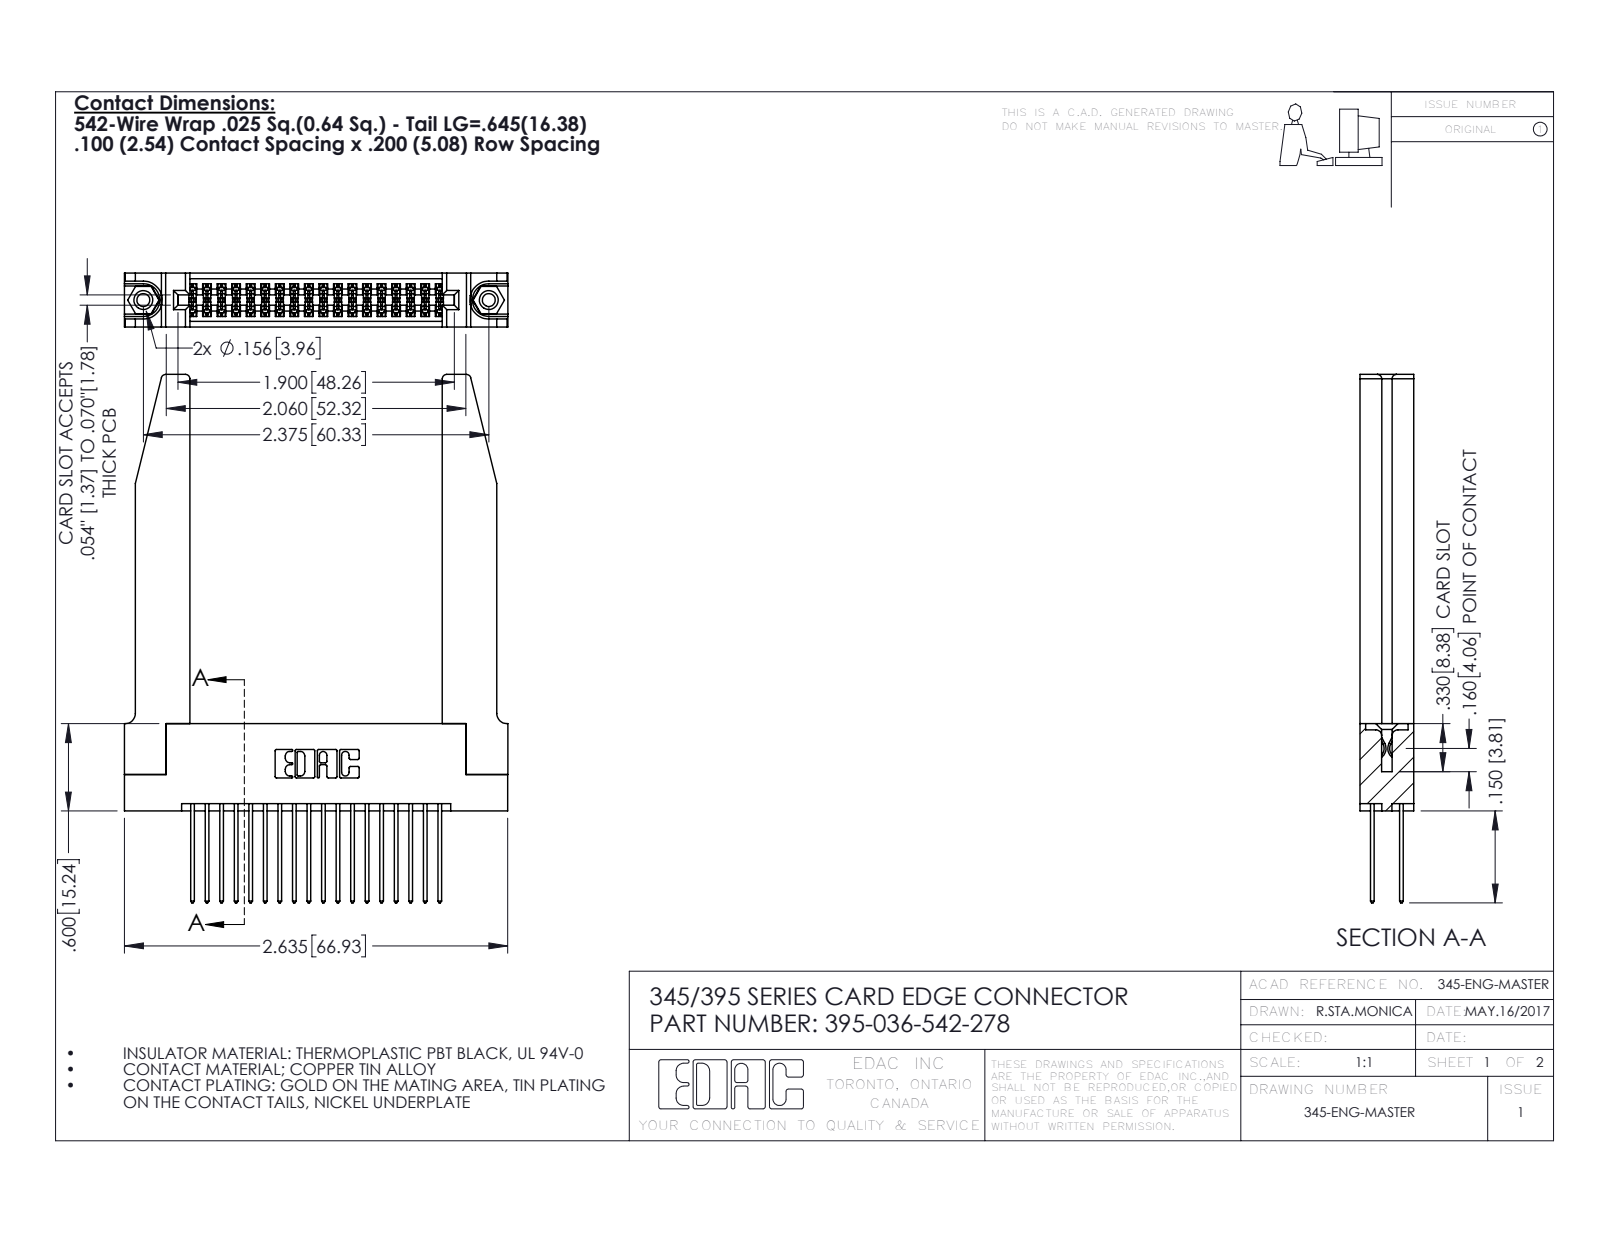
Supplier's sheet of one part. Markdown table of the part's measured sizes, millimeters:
| quantity | value |
| --- | --- |
| part name | 345-250-001_345-250-001-102; 345 Part_Flush Mounting Lugs - 0.156 Dia-TH; 345-220-078_345-220-078; 395-036-542-278 (+1 more) |
| STEP written by | SolidWorks 2016 (CONFIG_CONTROL_DESIGN) |
| units | millimeters |
| bodies | 41 solids, 2160 faces (1410 planar, 698 cylindrical, 52 other) |
| overall size | 92.3 × 67 × 9.4 |
| volume | 14 200 mm³ |
| surface area | 16 690 mm² |
| round holes (diameter × count) | 2.3 × 2, 3.2 × 2, 4 × 2, 1.6 × 1 |
| round bosses / shafts (diameter × count) | 3.9 × 2 |
| partial cylindrical surfaces (radius × count) | 0.2 × 54, 0.3 × 36, 0.3 × 22, 0.8 × 8, 0.2 × 6, 0.8 × 6, 0.7 × 3, 0.4 × 2 |
| main face-to-face distances | 9.4, 1.8, 7.6, 5.1, 2.5, 6.9, 0.6, 5.7, 3.8, 3.8 |
| hole center spacings | 6.9, 54.4, 60.3 |
